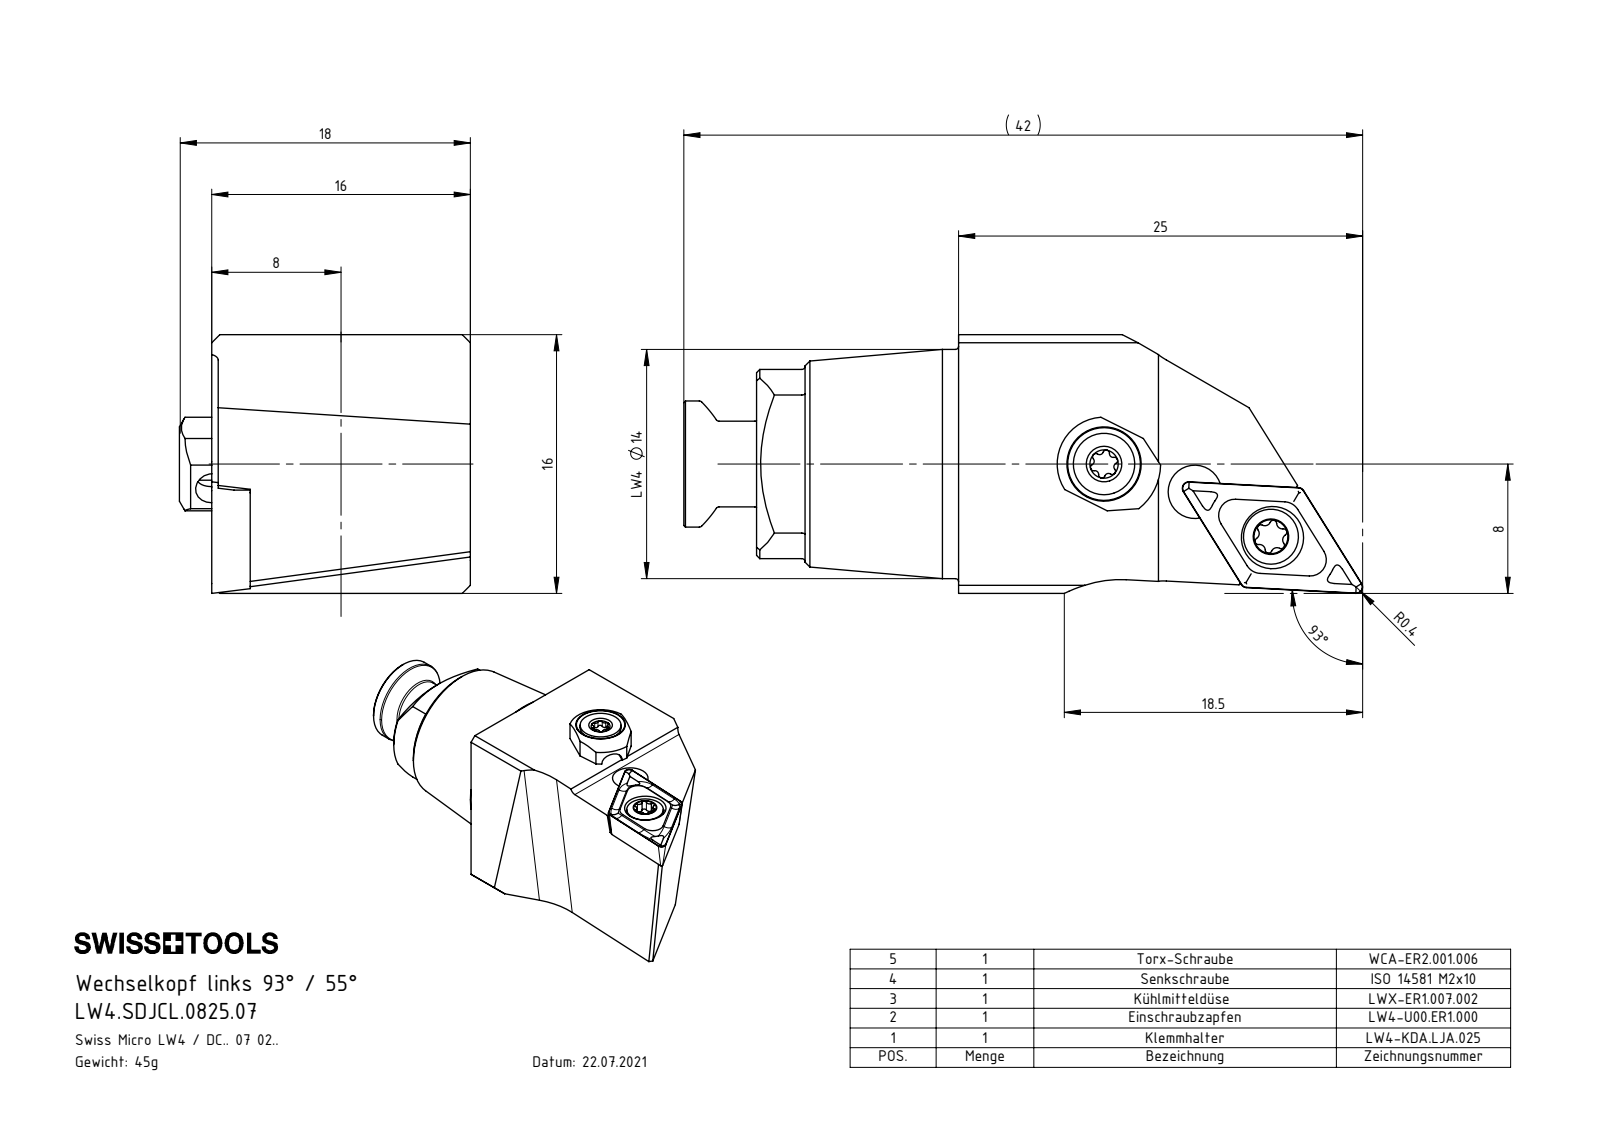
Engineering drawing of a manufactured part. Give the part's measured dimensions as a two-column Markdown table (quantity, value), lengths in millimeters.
| quantity | value |
| --- | --- |
| part name | LW4.SDJCL.0825.07; WCA-ER2.001.006_A; DCMT070204; LWX-ER1.007.002 (+3 more) |
| STEP written by | SolidWorks 2022 (CONFIG_CONTROL_DESIGN) |
| units | millimeters |
| bodies | 6 solids, 258 faces (70 planar, 80 cylindrical, 108 other) |
| overall size | 42 × 18 × 16 |
| volume | 5 812 mm³ |
| surface area | 3 361 mm² |
| round holes (diameter × count) | 3 × 2, 1.6 × 1, 2 × 1, 2.05 × 1, 2.5 × 1, 2.8 × 1, 3.3 × 1, 3.85 × 1, 5.5 × 1 |
| round bosses / shafts (diameter × count) | 14.17 × 1, 7.7 × 1, 6 × 1, 5.3 × 1, 5 × 1, 3.8 × 1, 3.4 × 1, 2.5 × 1 |
| partial cylindrical surfaces (radius × count) | 0.2 × 8, 0.21 × 6, 0.24 × 6, 0.36 × 4, 0.36 × 2, 0.5 × 1, 1 × 1, 2.9 × 1 |
| main face-to-face distances | 16, 13.62, 2.38, 15.6, 1.98, 0.4, 7.5, 2, 12.5, 4 |
| hole center spacings | 5.46, 5.57, 5.88, 11.26, 11.37 |
